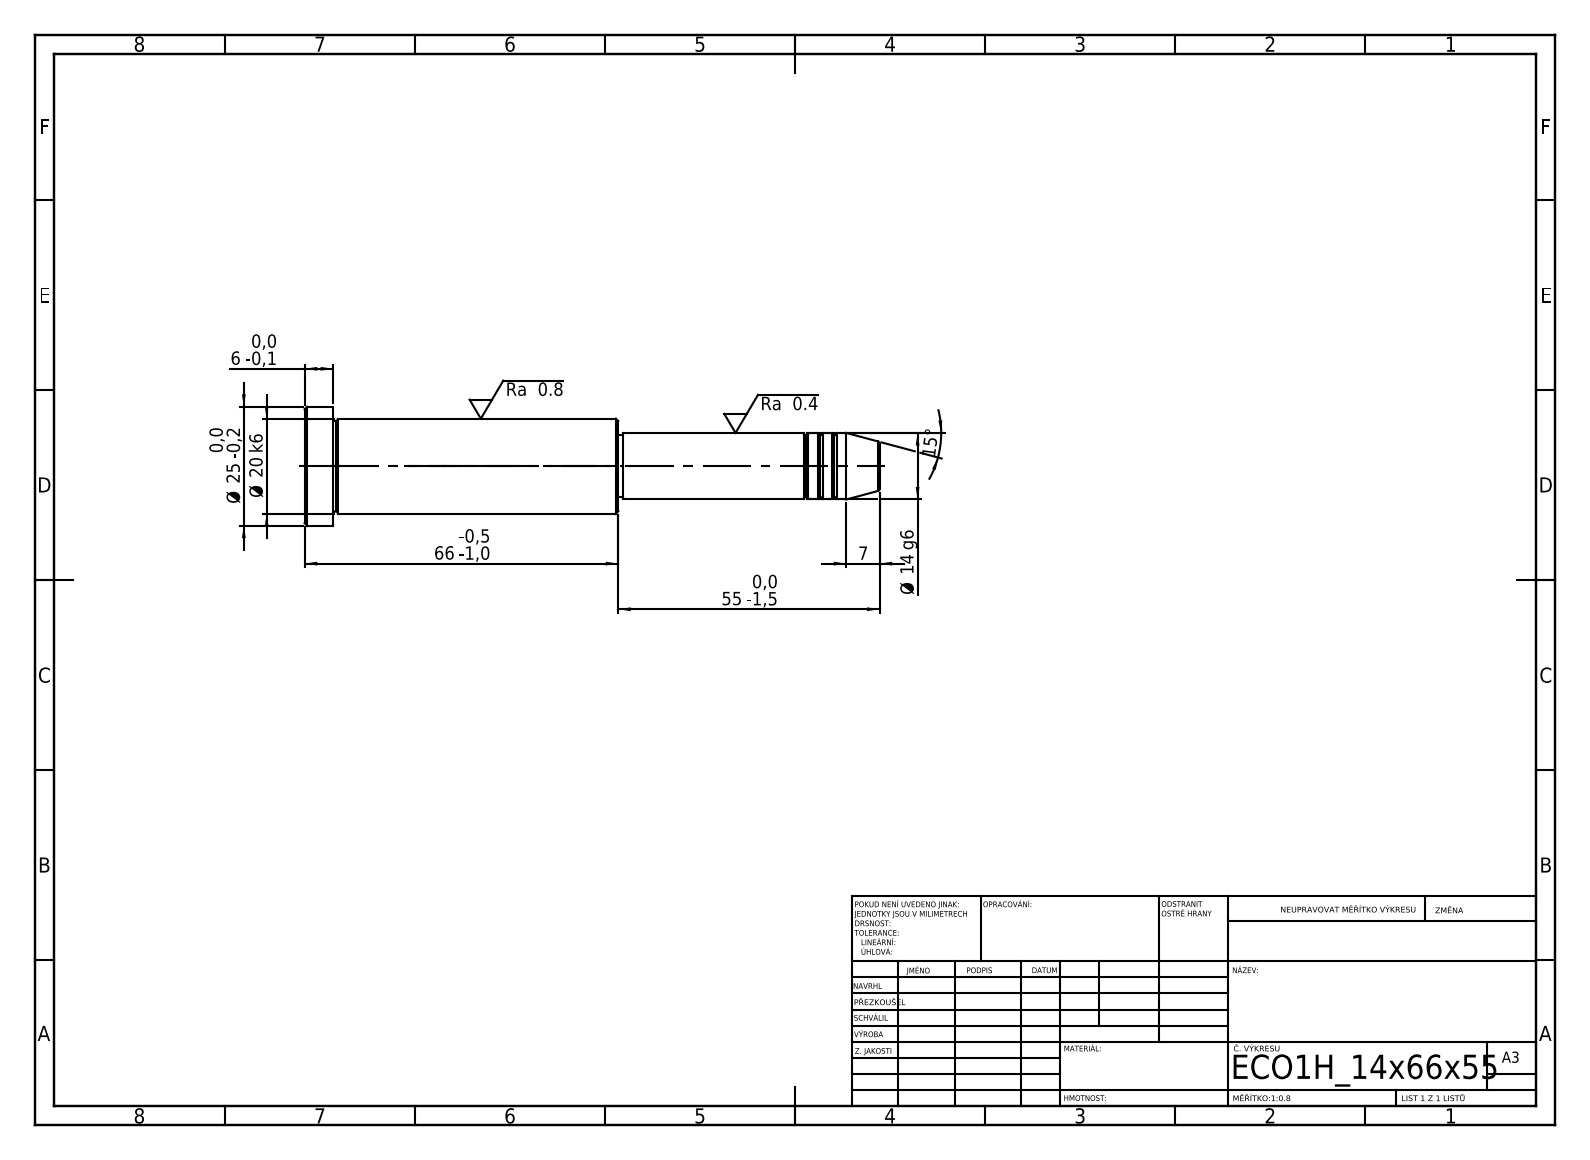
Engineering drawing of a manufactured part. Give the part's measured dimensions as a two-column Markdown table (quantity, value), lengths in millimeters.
| quantity | value |
| --- | --- |
| STEP written by | SolidWorks 2019 (CONFIG_CONTROL_DESIGN) |
| units | millimeters |
| bodies | 1 solid, 43 faces (5 planar, 14 cylindrical, 24 other) |
| overall size | 121 × 25 × 25 |
| volume | 29 885 mm³ |
| surface area | 7 631 mm² |
| round bosses / shafts (diameter × count) | 25 × 1, 20 × 1, 14 × 1, 13 × 1 |
| main face-to-face distances | 6, 60, 66, 55, 115, 121, 54, 1, 61, 67 |
